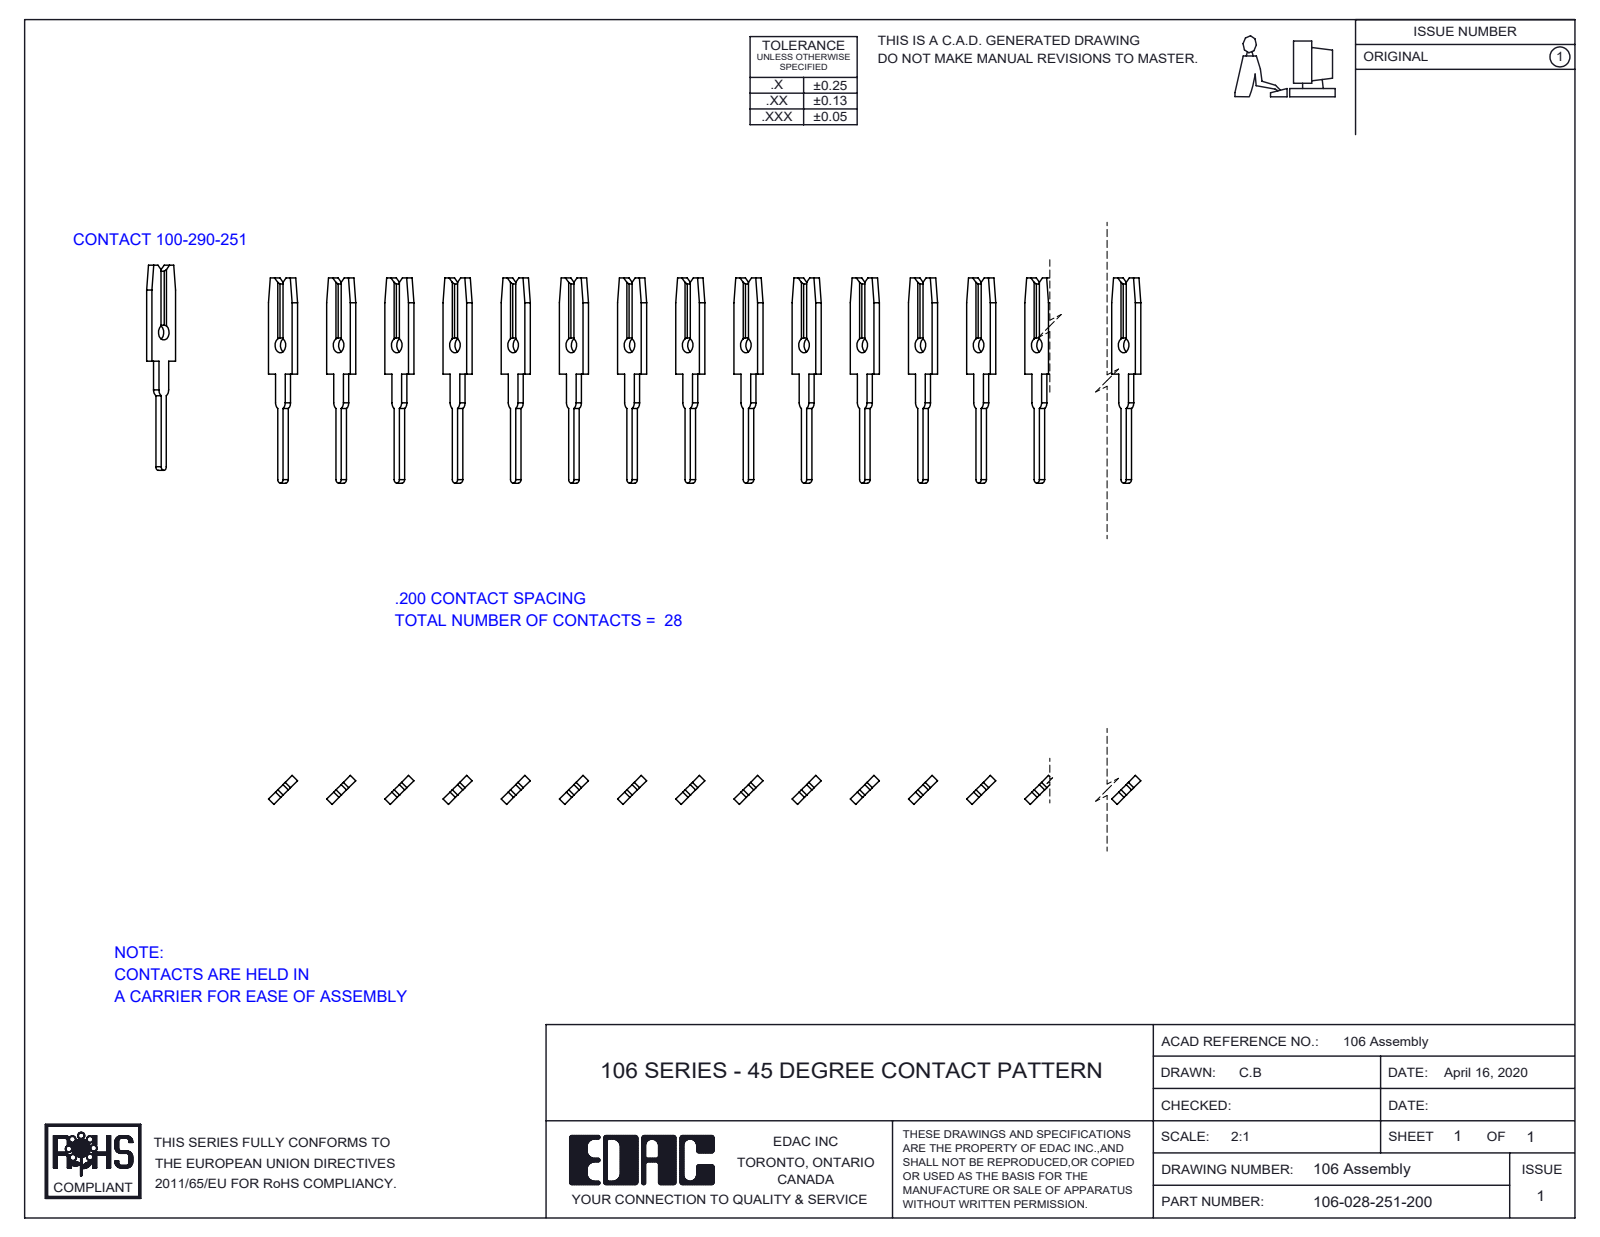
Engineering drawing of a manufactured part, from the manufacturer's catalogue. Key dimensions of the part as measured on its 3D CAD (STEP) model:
Part name (STEP PRODUCT): 106-028-251-200; 100-290-001_100-290-251
STEP written by: SolidWorks 2016 (CONFIG_CONTROL_DESIGN)
Units: inches
Bodies: 28 solids, 784 faces (616 planar, 168 cylindrical, 0 other)
Overall size (bounding box): 5.5 × 0.705 × 0.1
Volume: 0.031 in³ · Surface area: 3.9 in²
Round holes (diameter × count): ⌀0.052 ×28
Partial cylindrical surfaces — rounded edges, fillets, slot ends (radius × count): R0.012 ×28, R0.024 ×28
Main face-to-face distances: 0.141, 0.848, 0.707, 0.283, 0.99, 0.566, 0.424, 1.131, 0.424, 1.556
Hole centre spacings: 0.141, 0.283, 0.424, 0.848, 1.697, 1.839, 0.99, 1.556
